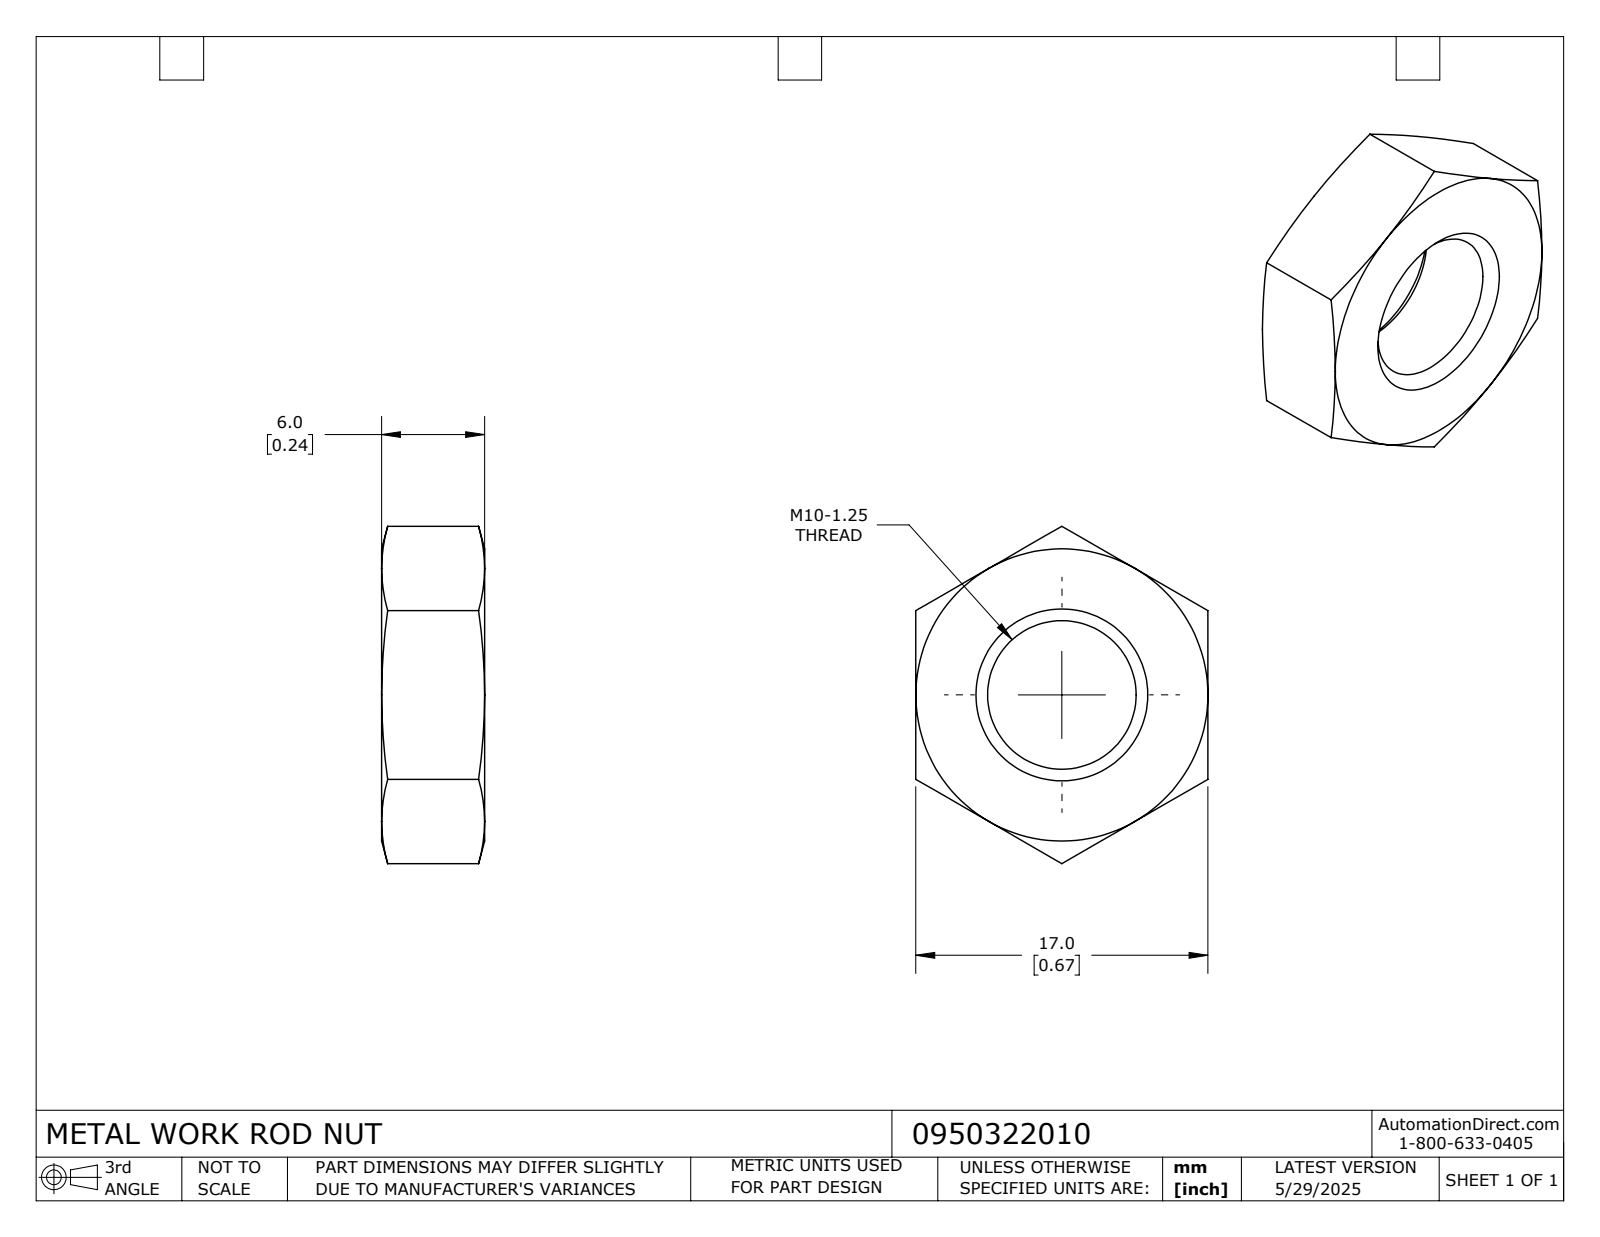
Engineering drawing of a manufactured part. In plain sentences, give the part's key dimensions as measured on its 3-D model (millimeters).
The part is named "0950322010". Its 3-D file was written by "SolidWorks 2024 (CONFIG_CONTROL_DESIGN)". It is 1 solid with 26 faces: 8 planar, 2 cylindrical and 16 other. Overall it measures 19.63 by 17 by 6 millimeters. Its volume is 1 131 cubic millimeters and its surface area 866 square millimeters. Round holes: 1 of diameter 8.65. The main face-to-face distances are 17, 6.
